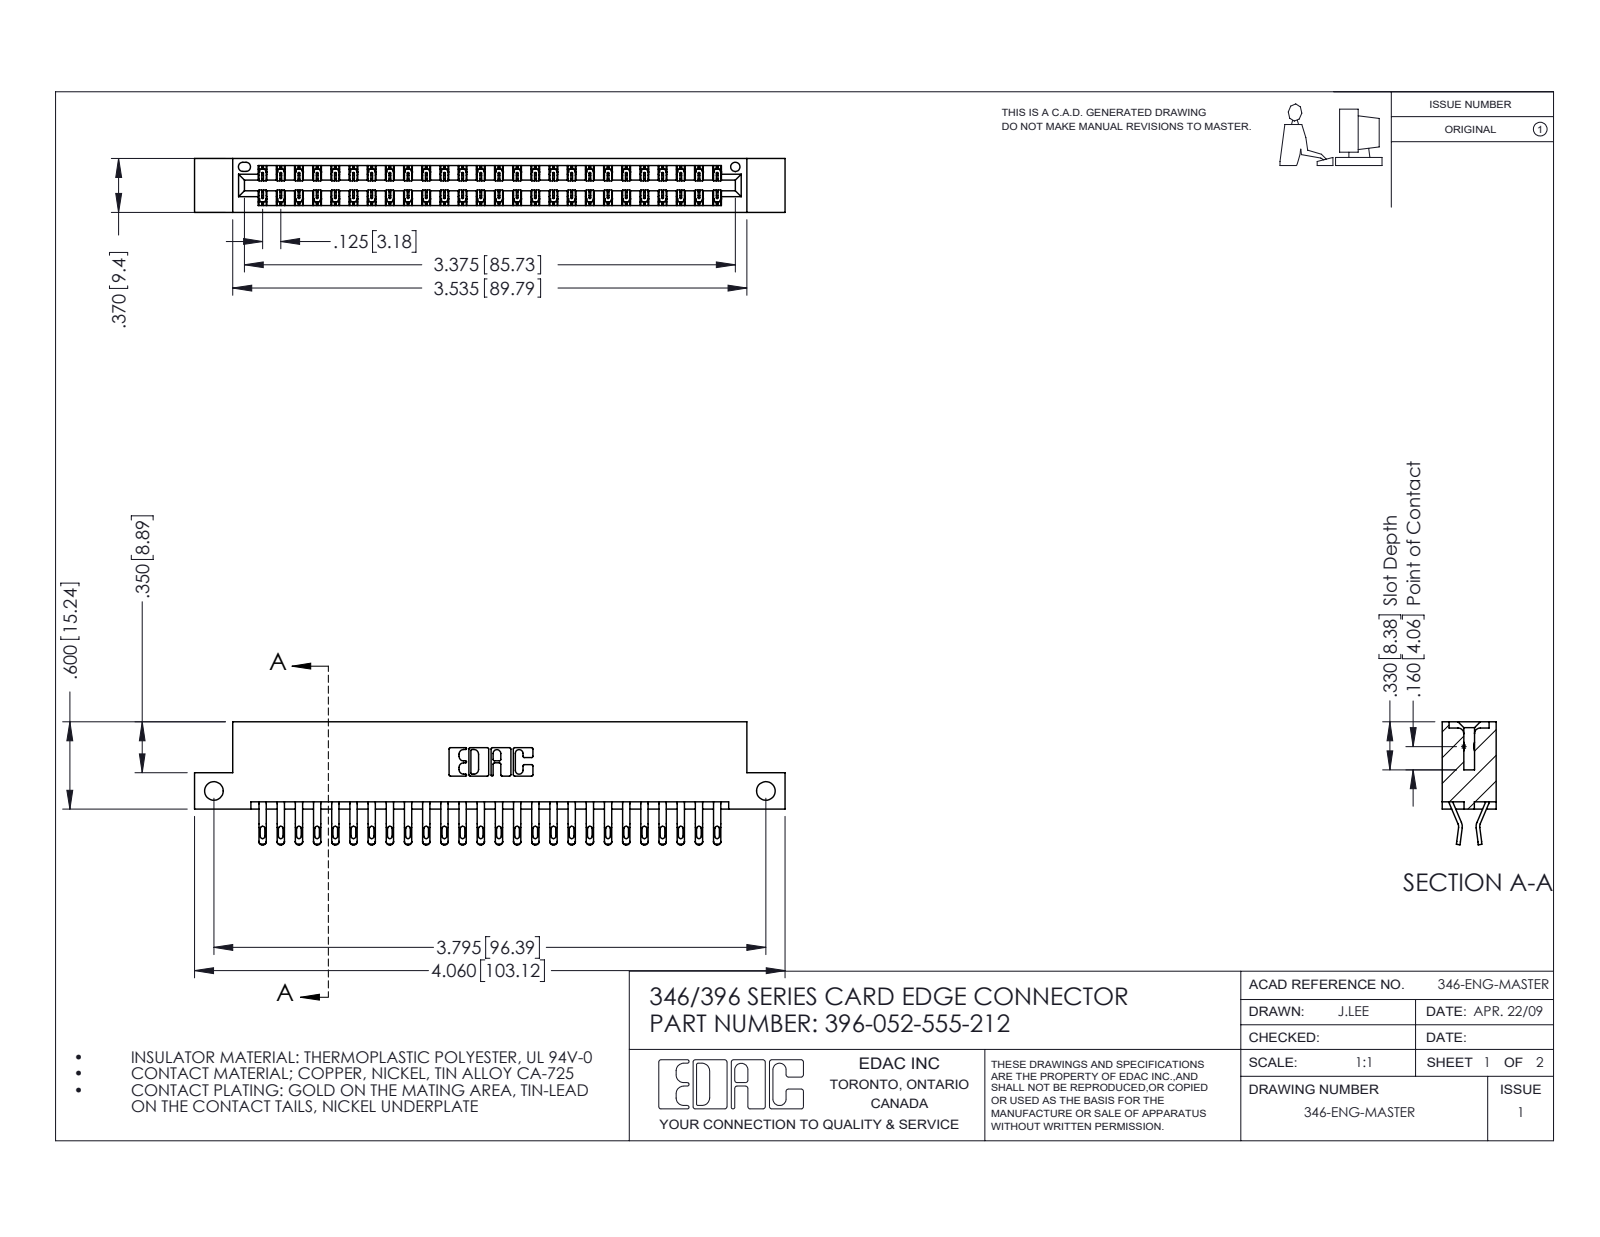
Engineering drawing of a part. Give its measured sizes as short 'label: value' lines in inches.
name: 345-292-001_555 Tail; 396-052-555-212; 346 Part_Flush Mounting Lugs - Side Mount
written by: SolidWorks 2016 (CONFIG_CONTROL_DESIGN)
unit: in
bodies: 53 solids, 3138 faces (1792 planar, 1346 cylindrical, 0 other)
size: 4.06 × 0.845 × 0.37
volume: 0.61 in³; area: 21.53 in²
holes: 2× ⌀0.128, 1× ⌀0.064
rounds: 104× R0.016, 104× R0.02, 78× R0.006, 22× R0.01, 6× R0.007, 6× R0.031, 3× R0.026, 2× R0.01
face distances: 0.048, 0.322, 0.25, 0.37, 0.025, 0.072, 0.298, 0.275, 0.148, 0.222
hole spacings: 3.795
